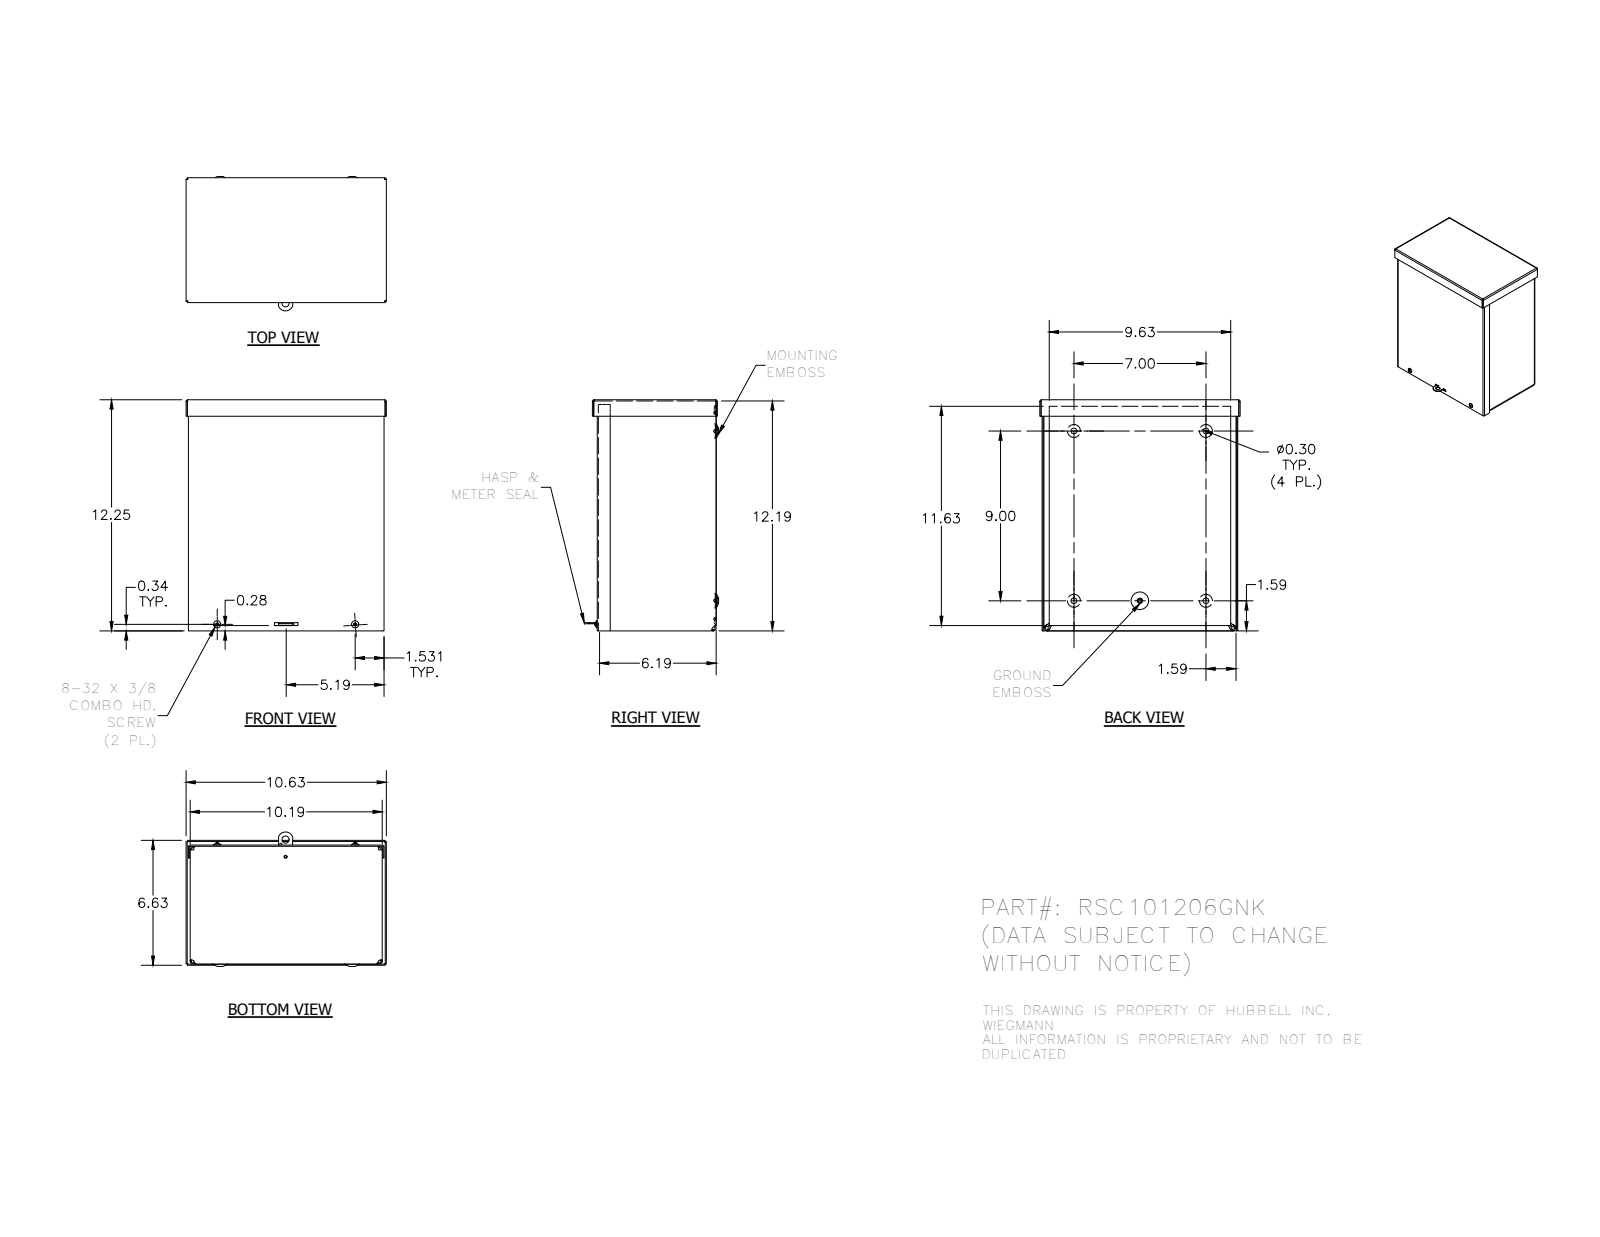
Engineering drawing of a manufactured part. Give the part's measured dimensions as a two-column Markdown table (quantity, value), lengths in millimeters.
| quantity | value |
| --- | --- |
| part name | RSC101206GNK_WRAP; RSC1012GNK_LID; RSC1006GNK_CAP; 3183 (+3 more) |
| STEP written by | Autodesk Inventor 2014 (AUTOMOTIVE_DESIGN) |
| units | millimeters |
| bodies | 7 solids, 377 faces (163 planar, 78 cylindrical, 136 other) |
| overall size | 311.16 × 269.88 × 180.97 |
| volume | 696 338 mm³ |
| surface area | 894 158 mm² |
| round holes (diameter × count) | 7.62 × 4, 7.95 × 4, 3.17 × 2, 3.76 × 2, 3.96 × 1, 4.19 × 1, 9.52 × 1 |
| round bosses / shafts (diameter × count) | 9.75 × 2, 4.17 × 2, 5.8 × 1 |
| partial cylindrical surfaces (radius × count) | 0.79 × 8, 2.37 × 8, 3.17 × 8, 4.75 × 8, 1.4 × 4, 1.57 × 4, 2.38 × 4, 2.97 × 4 |
| main face-to-face distances | 1.58, 1.57, 257.19, 158.73, 157.15, 307.99, 1.59, 160.32, 158.74, 3.15 |
| hole center spacings | 27.24, 32.03, 88.9, 177.8, 185.75, 228.6, 245.27, 255.58 |
